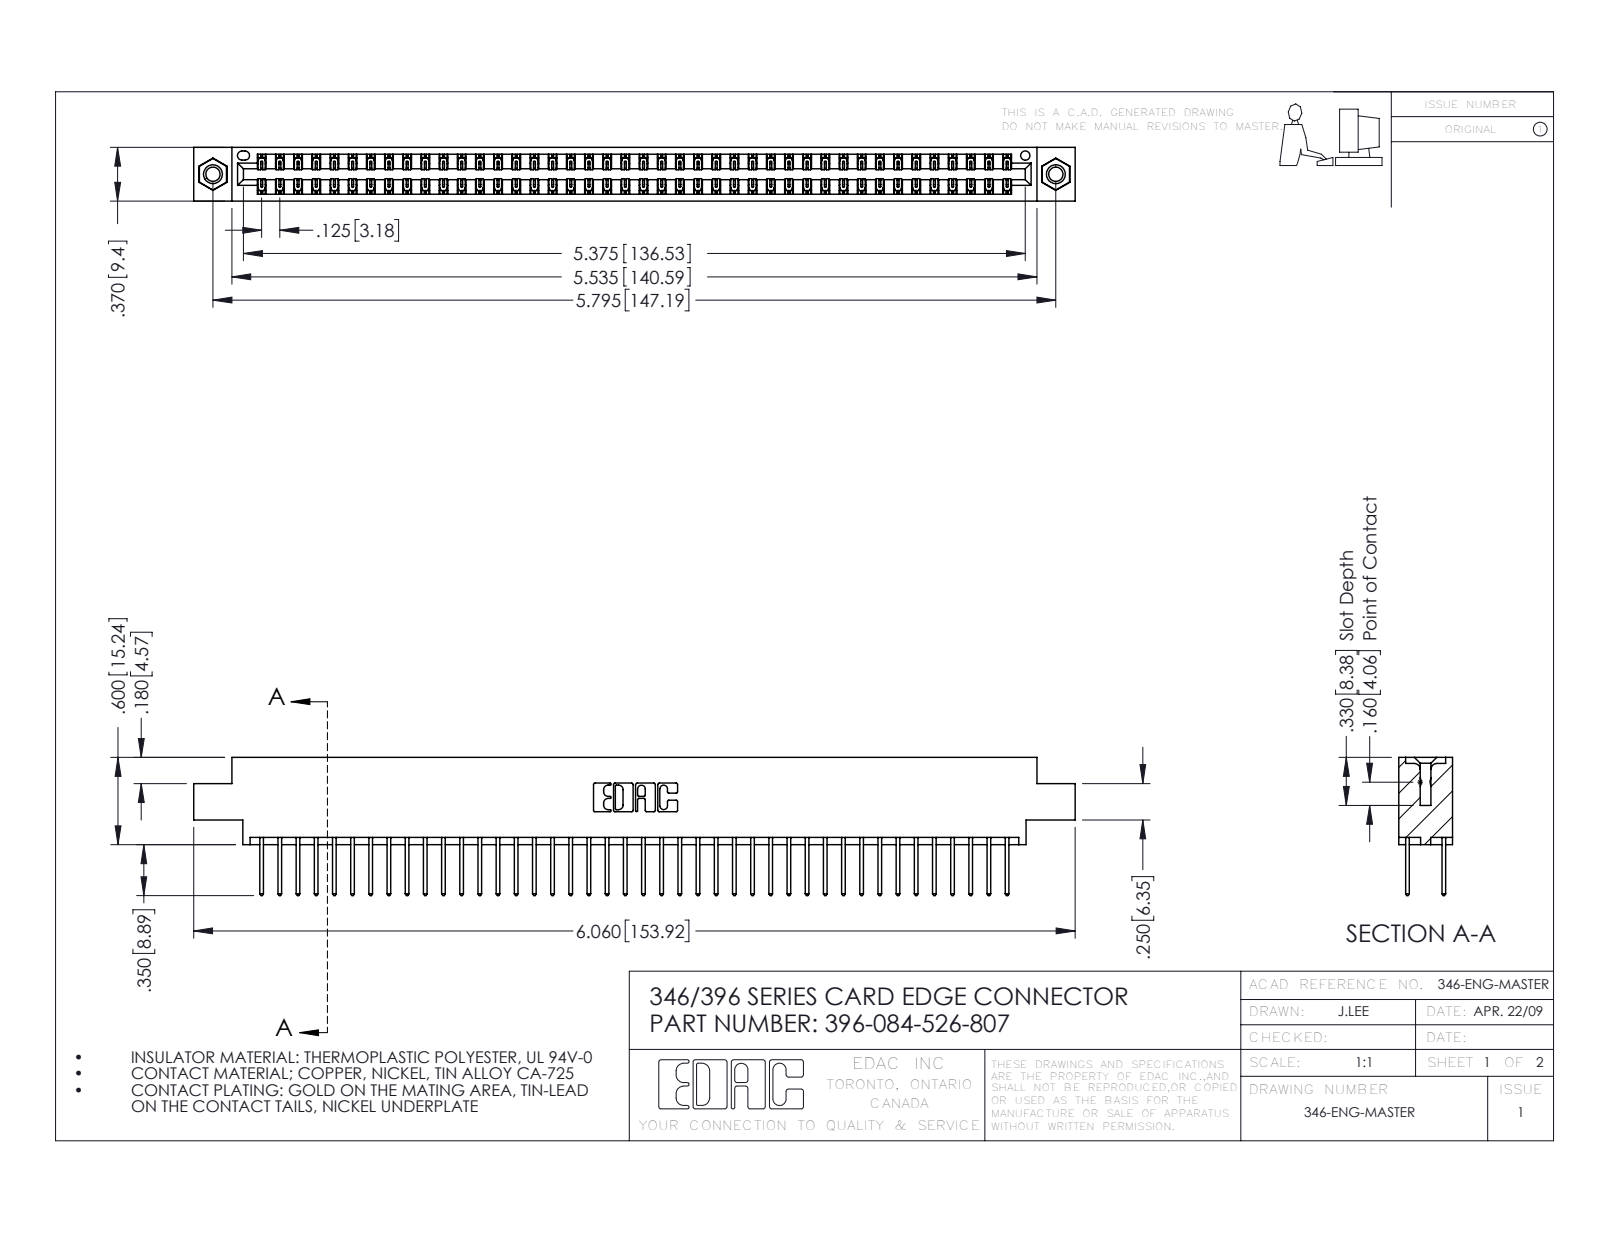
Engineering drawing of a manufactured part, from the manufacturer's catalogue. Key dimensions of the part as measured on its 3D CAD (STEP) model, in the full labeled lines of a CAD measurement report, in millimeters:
Part name (STEP PRODUCT): 396-084-526-807; 345-292-001_345-293-126; 345-250-001_345-250-005-103; 346 Part_0.170 Offset - 0.156 Dia-TI
STEP written by: SolidWorks 2016 (CONFIG_CONTROL_DESIGN)
Units: millimetres
Bodies: 87 solids, 4554 faces (3052 planar, 1486 cylindrical, 16 other)
Overall size (bounding box): 153.9 × 24.1 × 9.4
Volume: 15 000 mm³ · Surface area: 21 420 mm²
Round holes (diameter × count): ⌀2.5 ×2, ⌀3.2 ×2, ⌀4 ×2, ⌀1.6 ×1
Round bosses / shafts (diameter × count): ⌀3.9 ×2
Partial cylindrical surfaces — rounded edges, fillets, slot ends (radius × count): R0.2 ×126, R0.3 ×84, R0.3 ×22, R0.2 ×6, R0.8 ×6, R0.7 ×3, R0.4 ×2, R0.6 ×2
Main face-to-face distances: 1.2, 8.2, 6.4, 9.4, 1.8, 7.6, 0.6, 7, 5.6, 3.8
Hole centre spacings: 6.2, 141.9, 147.2
